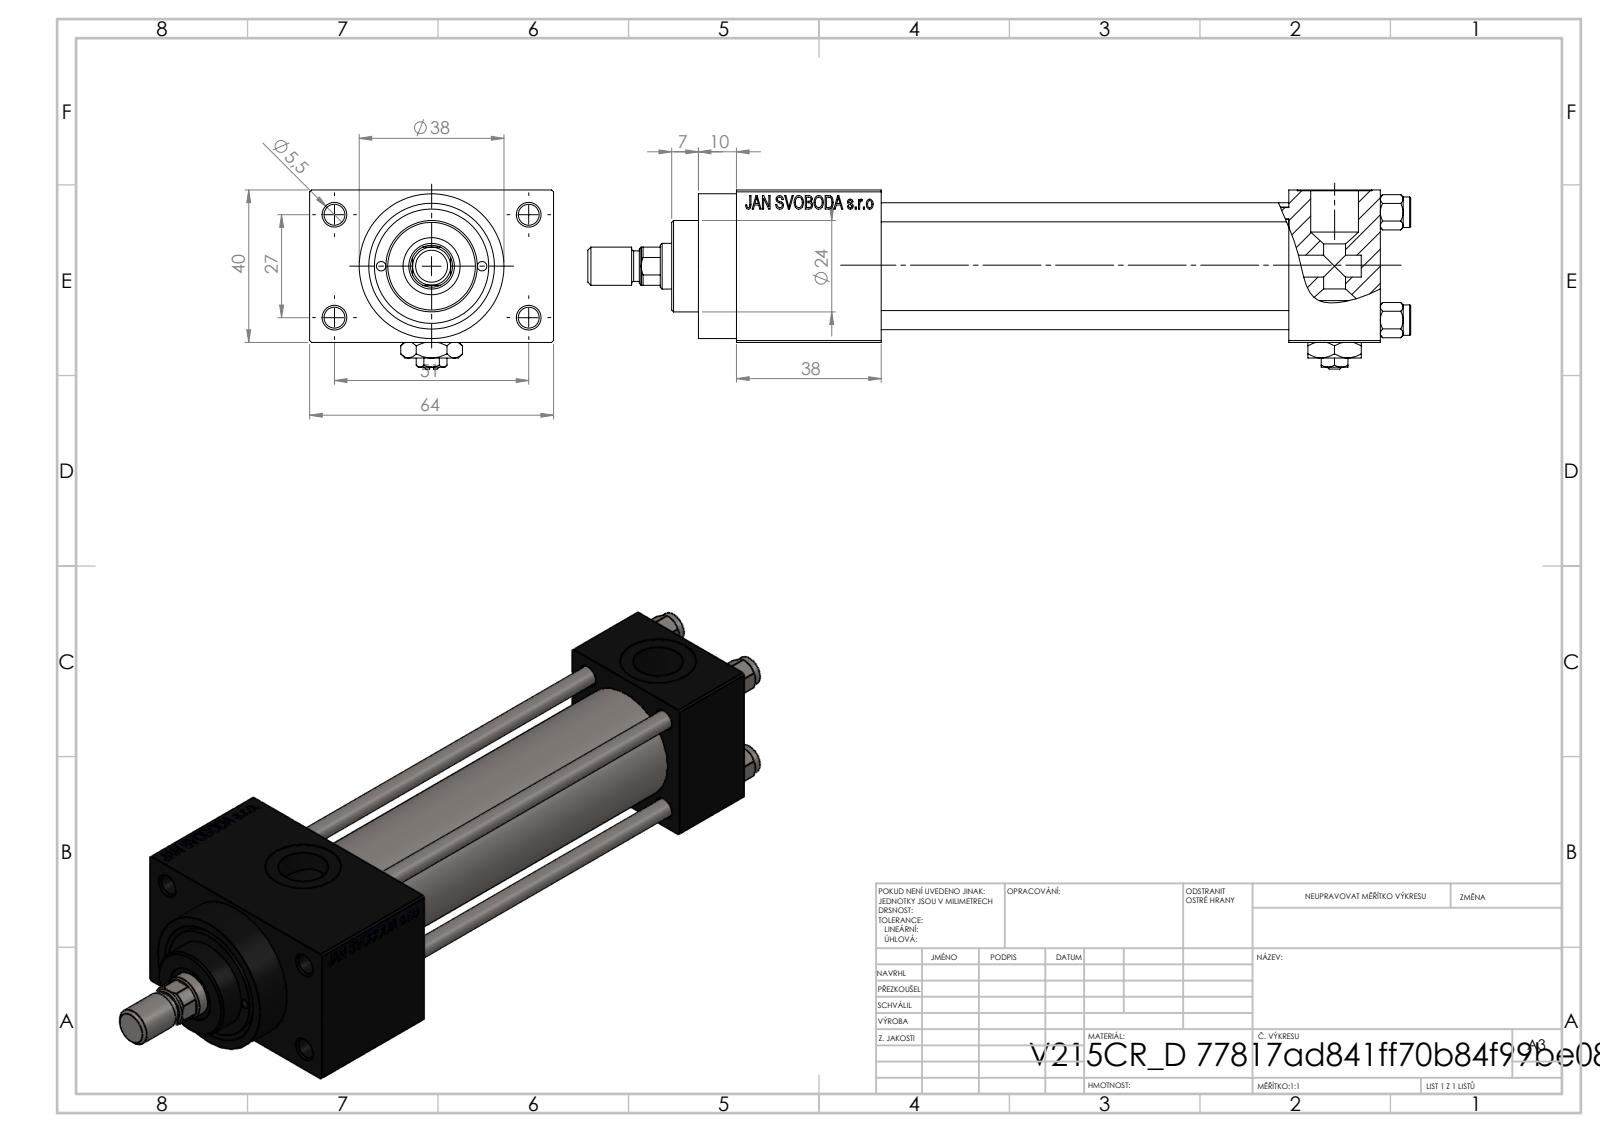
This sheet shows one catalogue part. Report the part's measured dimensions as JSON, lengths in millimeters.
{"part_name": "Zatka_pro_OIL_PORT; NUT_M5_D; V215CR_D_TYCINKA; V215CR_D_Body (+3 more)", "step_written_by": "SolidWorks 2019 (CONFIG_CONTROL_DESIGN)", "units": "millimeters", "bodies": {"solids": 13, "faces": 1177, "planar": 525, "cylindrical": 104, "other": 548}, "overall_size": [216, 64, 47], "volume_mm3": 202364, "surface_area_mm2": 79949, "round_holes": [[5, 4], [5.5, 4], [20, 3], [2.5, 2], [7, 2], [13.16, 2], [6.5, 1], [12, 1], [15, 1], [25, 1], [30, 1]], "round_bosses_or_shafts": [[8, 5], [38, 1], [31, 1], [24, 1], [10, 1]], "partial_cylinders_radius": [[5.5, 1]], "face_to_face_distances": [40, 12, 52, 107, 24, 131, 64, 38, 169, 145], "hole_center_spacings": [11.37, 14.18, 18.23, 20.01, 28.3, 28.85, 29.89, 30.84]}
